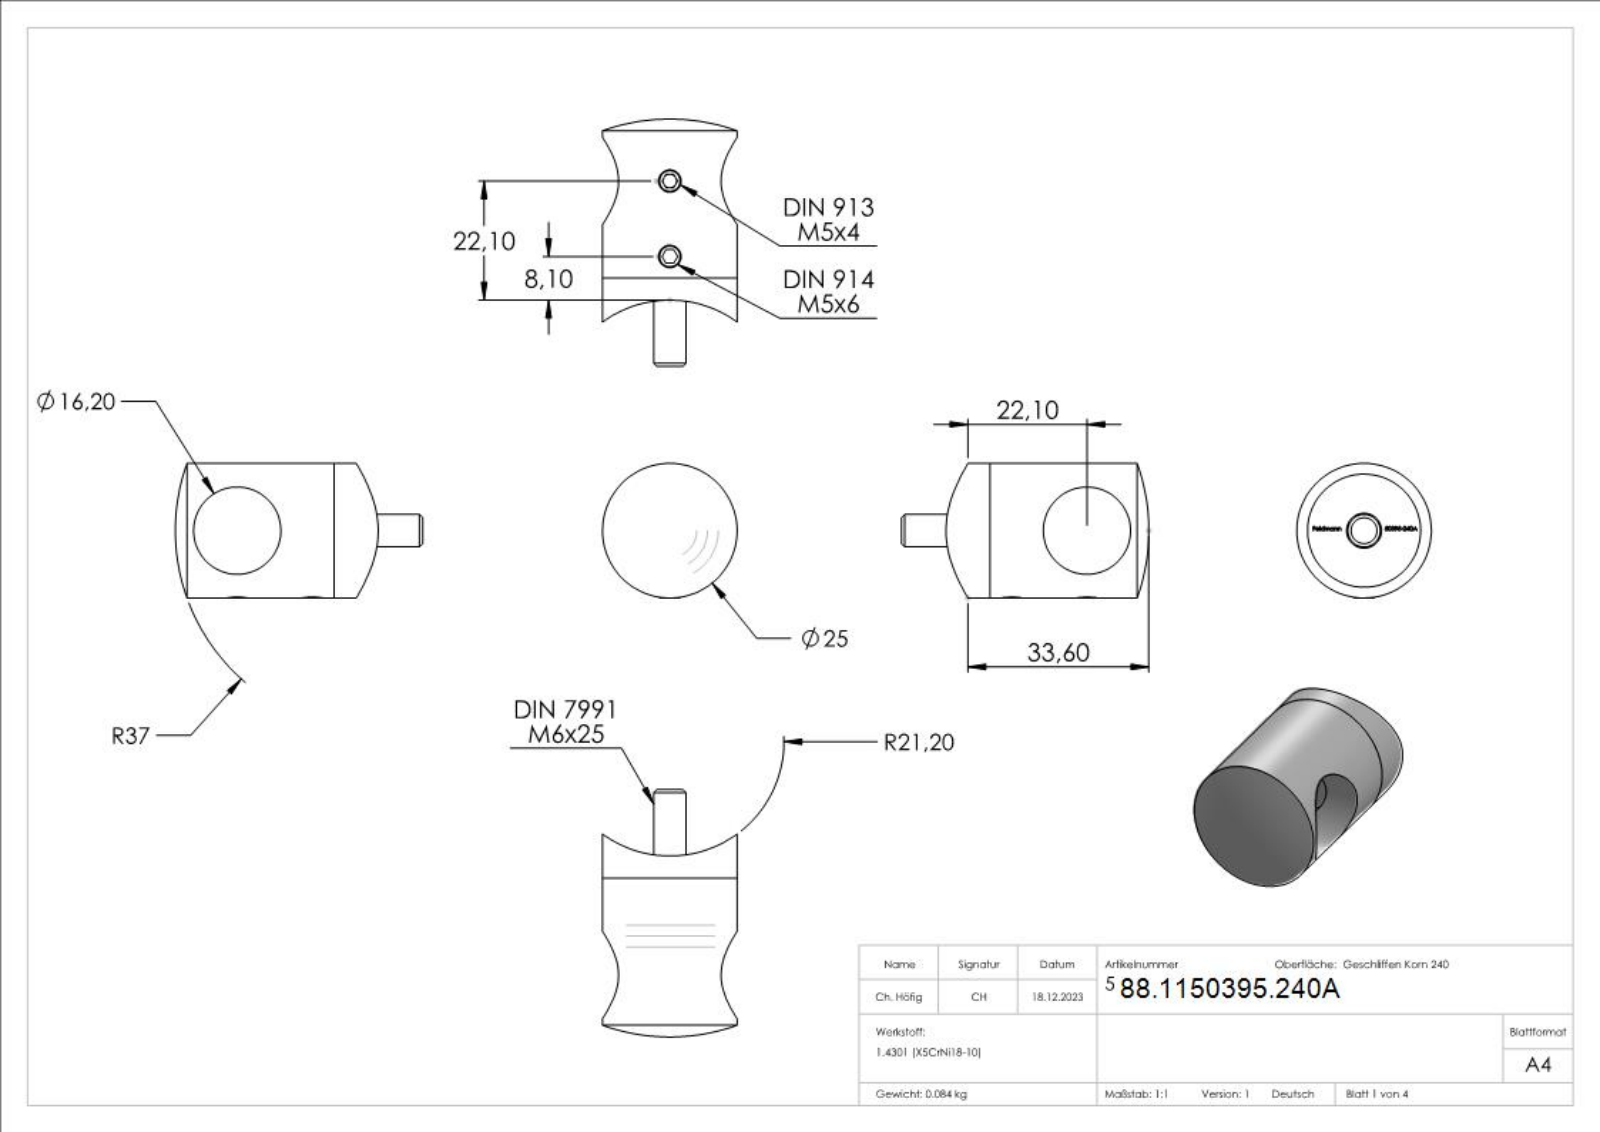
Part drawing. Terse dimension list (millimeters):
name: DIN914_DIN 914 M5x6; DIN913; DIN7991 M6x25; DIN914 (+7 more)
written by: SolidWorks 2018 (CONFIG_CONTROL_DESIGN)
unit: mm
bodies: 5 solids, 340 faces (173 planar, 30 cylindrical, 137 other)
size: 70 × 45.95 × 25
volume: 10 625 mm³; area: 7 167 mm²
holes: 2× ⌀4.2, 1× ⌀6.5, 1× ⌀16.2, 1× ⌀21
bosses: 2× ⌀5, 1× ⌀25, 1× ⌀12, 1× ⌀6
rounds: 1× R21.2
face distances: 2, 10.55, 8.55, 9.5, 7.5, 4, 1.05, 2.5, 14.45, 16.45
hole spacings: 14
